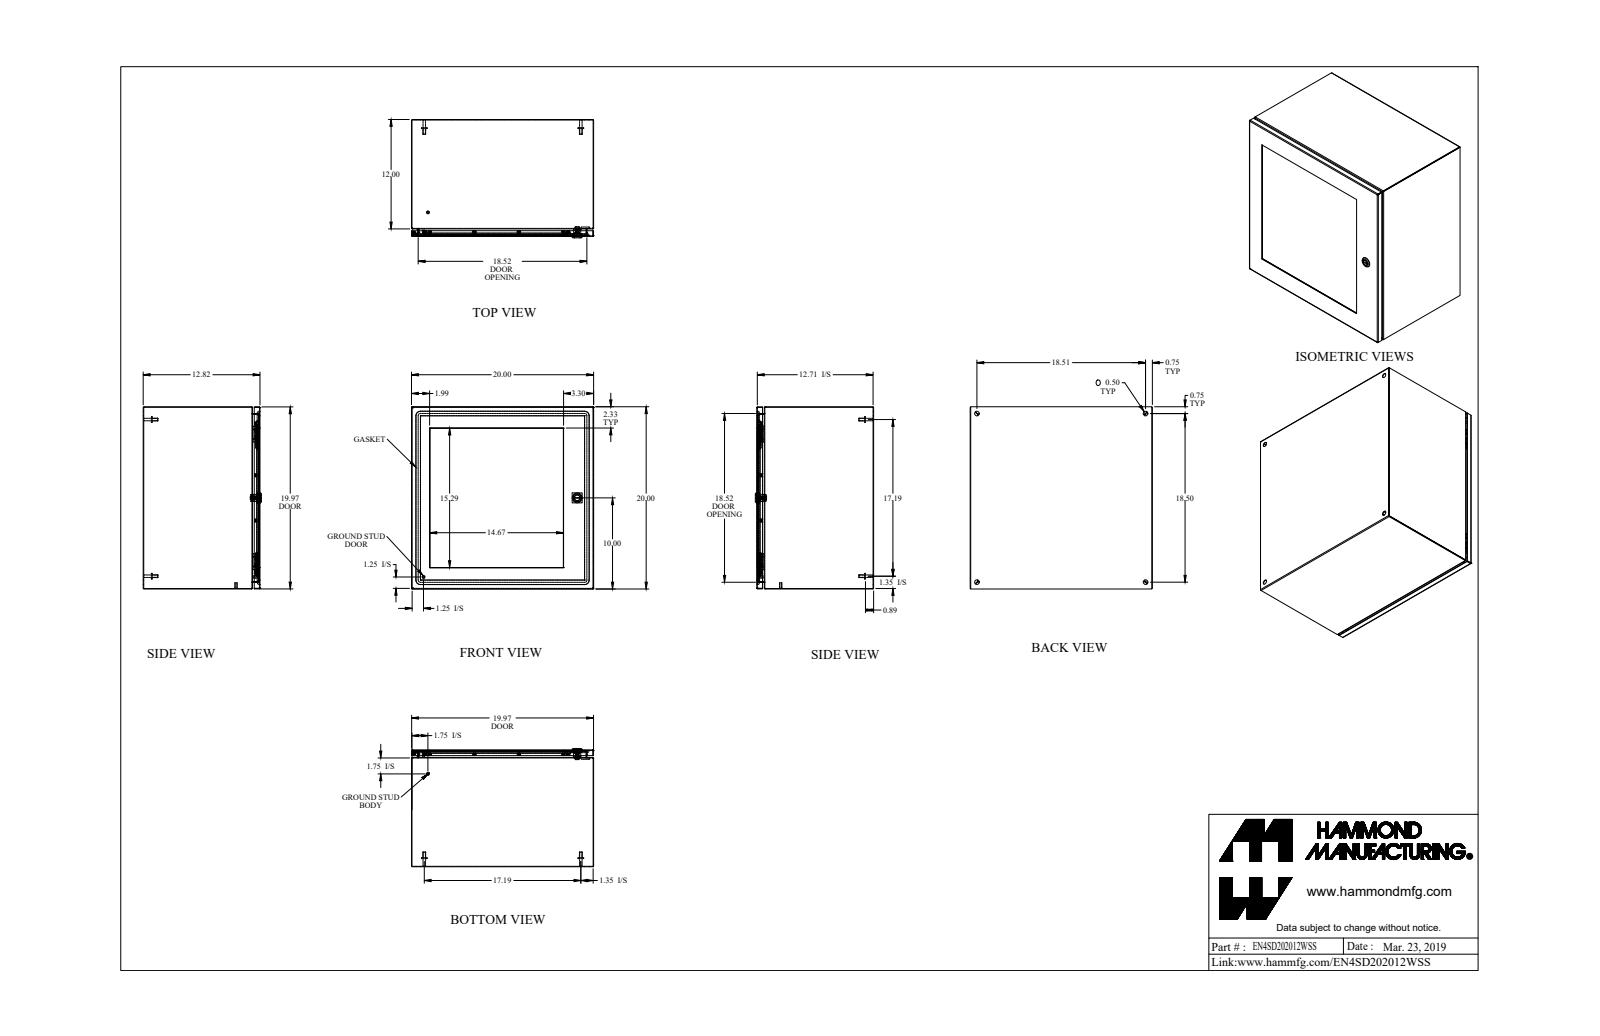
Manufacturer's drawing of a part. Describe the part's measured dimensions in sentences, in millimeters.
The part is named "EN4SD202012WSS_Default". Its 3-D file was written by "SolidWorks 2019 (CONFIG_CONTROL_DESIGN)". It is 65 solids with 1275 faces: 646 planar, 383 cylindrical and 246 other. Overall it measures 508 by 508 by 329.7 millimeters. Its volume is 2 786 000 cubic millimeters and its surface area 2 750 000 square millimeters. Round holes: 16 of diameter 3.3, 16 of diameter 6.4, 5 of diameter 12.7, 1 of diameter 4.4, 1 of diameter 5, 1 of diameter 6.1, 1 of diameter 6.1, 1 of diameter 9.8, 1 of diameter 16, 1 of diameter 19.5. Round bosses or shafts: 17 of diameter 5.7, 16 of diameter 9.3, 16 of diameter 4.2, 6 of diameter 8, 4 of diameter 15.9, 4 of diameter 7, 2 of diameter 6.4, 1 of diameter 27.9. Partial cylindrical surfaces (rounded edges, fillets, slot ends): 19 of radius 0.7, 19 of radius 2.2, 12 of radius 4.8, 10 of radius 3.2, 4 of radius 0.2, 4 of radius 0.4, 4 of radius 1.6, 4 of radius 2.2. The main face-to-face distances are 1.4, 506.6, 324.2, 505.1, 508, 322.8, 6.4, 316.4, 317.9, 7.8. The hole center spacings are 248.4, 414.9, 124.2, 124.2, 124.2, 124.2, 262.2, 418.4.
